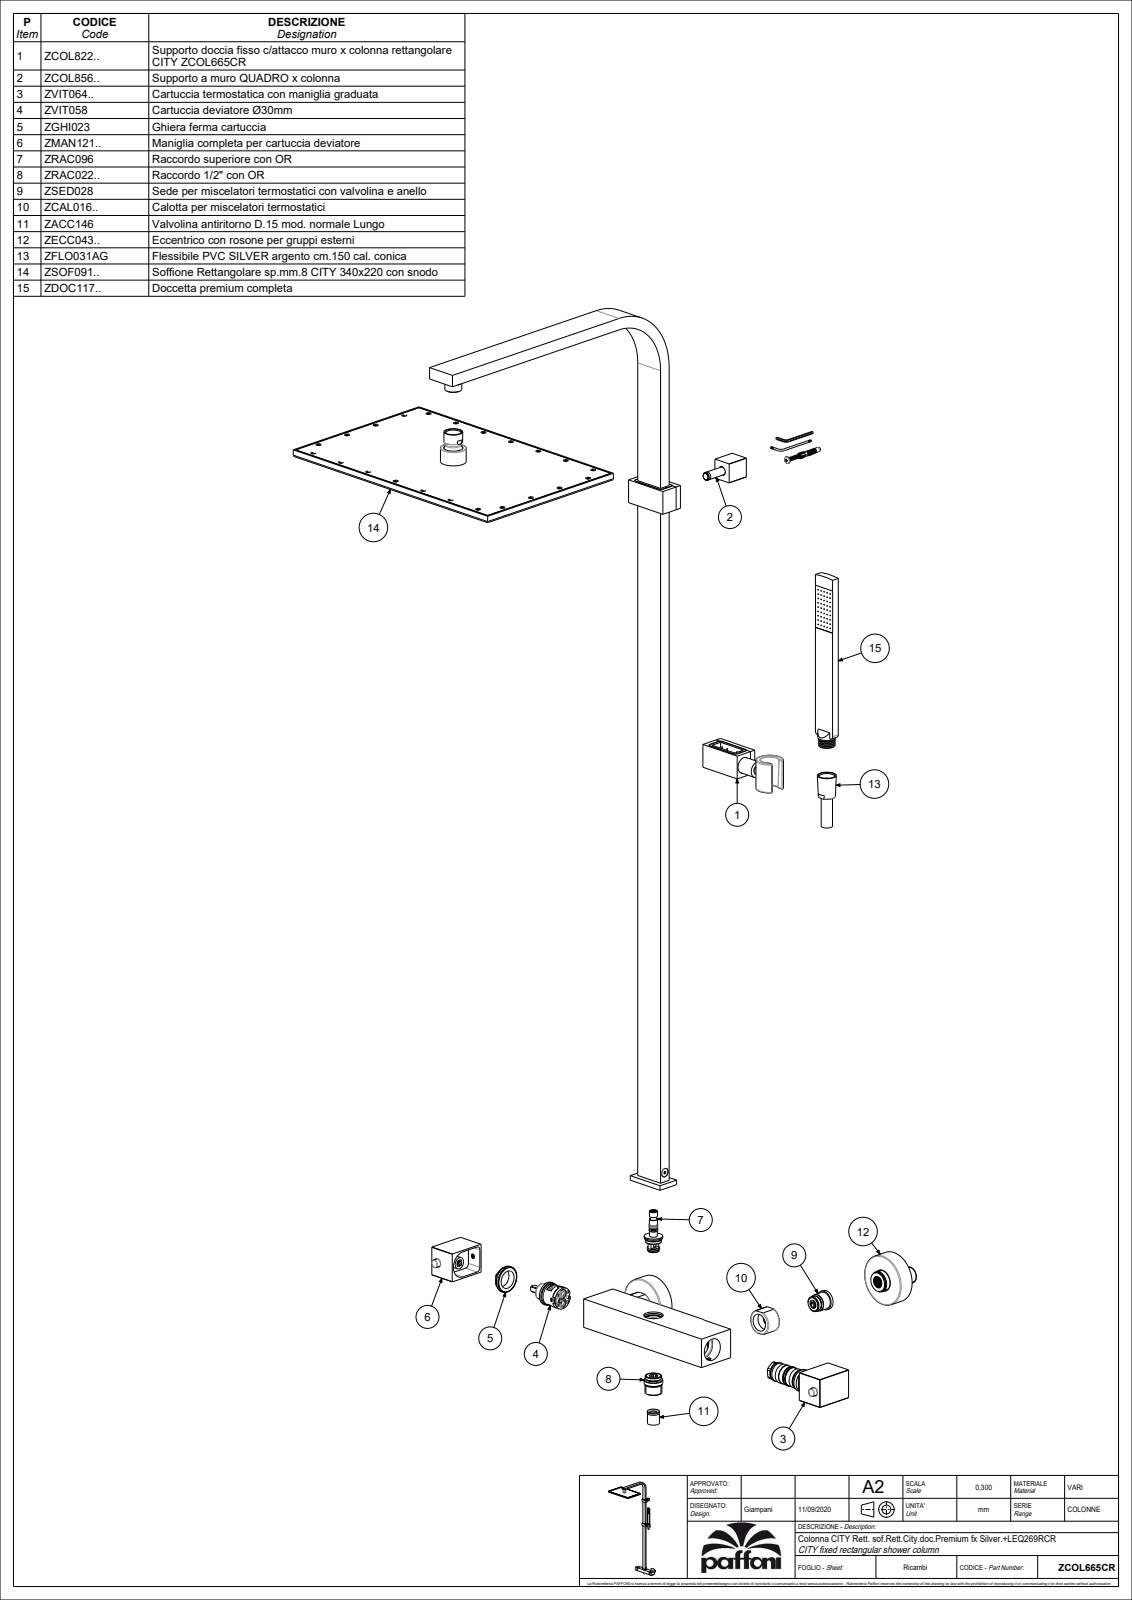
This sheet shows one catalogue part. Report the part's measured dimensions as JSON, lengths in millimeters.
{"part_name": "ZCOL665CR_SW0001; 4071860CR-A-1; 4071860CR-A-2; 4071860CR-A_ASM (+8 more)", "step_written_by": "CREO PARAMETRIC BY PTC INC, 2020044 (CONFIG_CONTROL_DESIGN)", "units": "millimeters", "bodies": {"solids": 175, "faces": 9739, "planar": 2462, "cylindrical": 3528, "other": 3749}, "overall_size": [1215.5, 535.7, 340], "volume_mm3": 950642, "surface_area_mm2": 999574, "round_holes": [[0.8, 324], [3.3, 116], [1.5, 112], [1.7, 112], [2.5, 25], [7, 24], [5.1, 22], [5.5, 10], [4.5, 7], [3.5, 4], [4.2, 4], [6, 4]], "round_bosses_or_shafts": [[5, 143], [10, 114], [6, 23], [4.3, 22], [3, 22], [0.4, 22], [2, 11], [27, 3]], "partial_cylinders_radius": [[1, 112], [0.5, 92], [0.2, 59], [20, 22], [4, 20], [5, 11], [0.3, 8], [0.8, 8]], "face_to_face_distances": [1.5, 13.5, 6, 7.5, 1, 7, 8.5, 15, 12, 38.5], "hole_center_spacings": [48, 207.14, 96, 223.2, 17.03, 40.52, 144, 247.67]}
